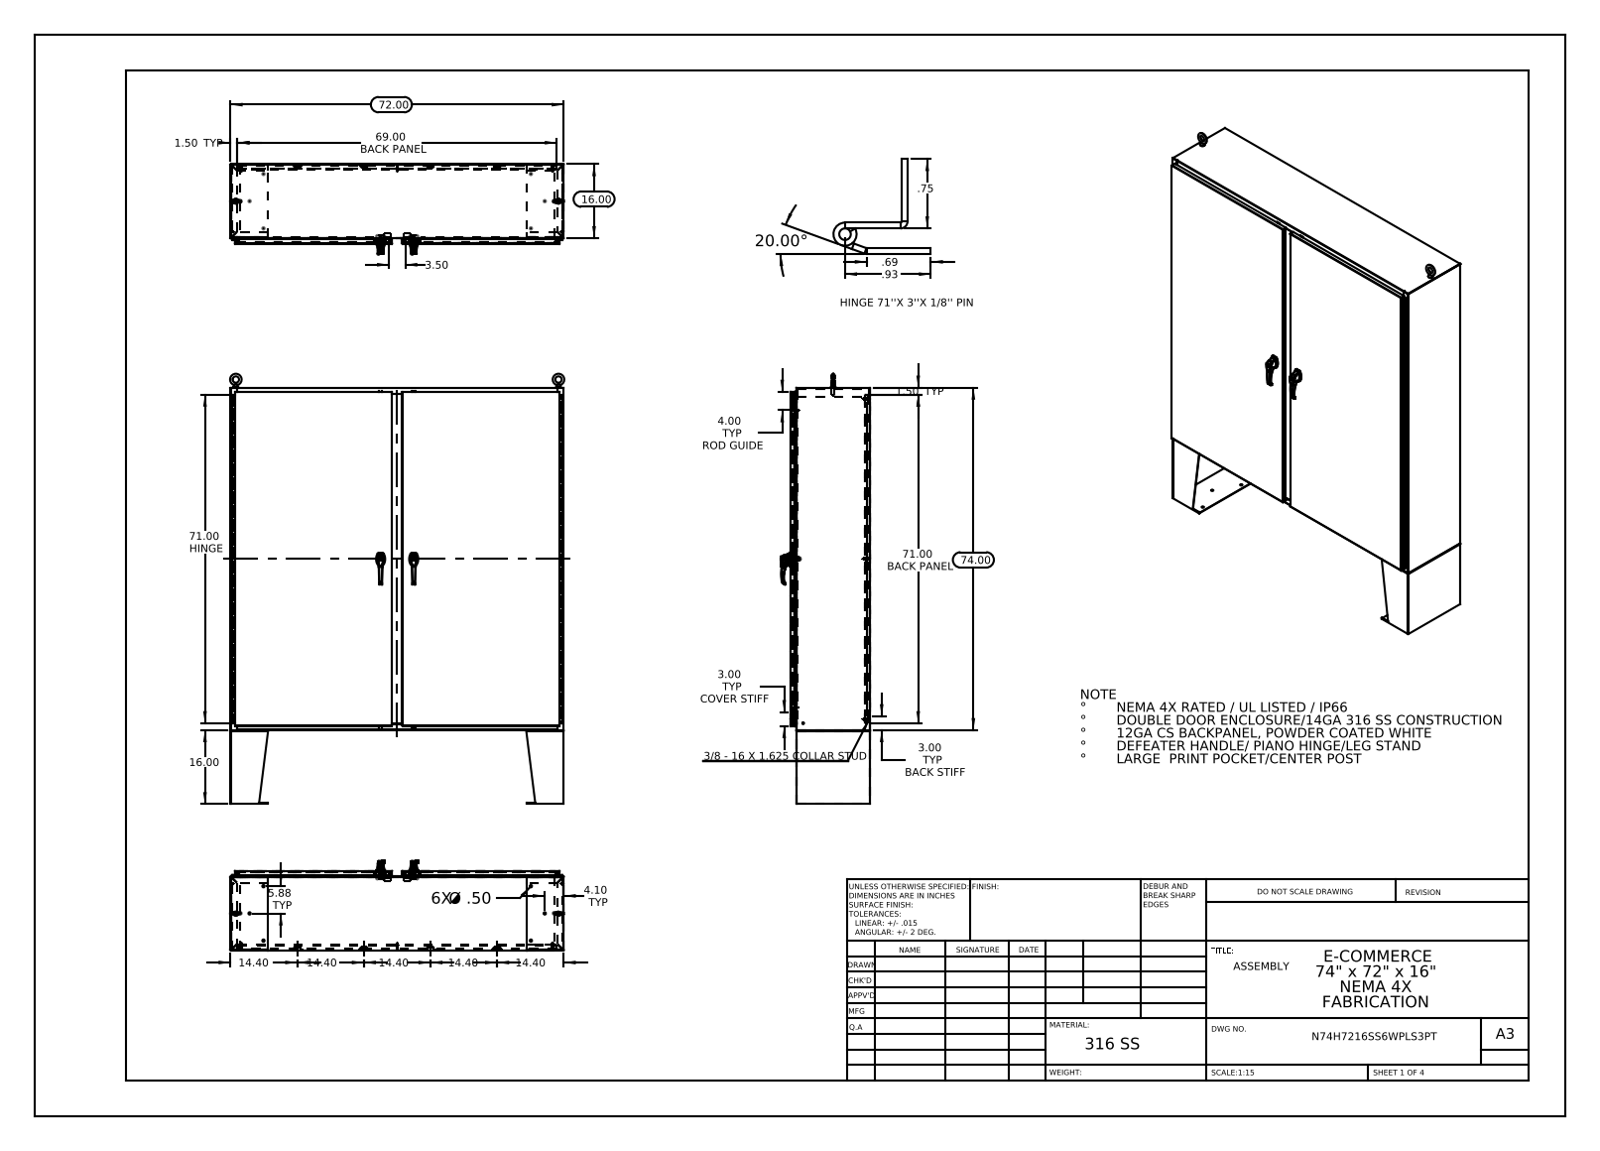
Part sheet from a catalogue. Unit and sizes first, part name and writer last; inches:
Units: inches
Overall size (bounding box): 93 × 72.226 × 19.307
Round holes (diameter × count): ⌀0.25 ×20, ⌀0.5 ×14, ⌀0.138 ×6, ⌀0.161 ×6, ⌀0.079 ×4, ⌀0.313 ×4, ⌀0.437 ×4, ⌀0.75 ×4, ⌀0.125 ×2, ⌀0.125 ×2, ⌀0.197 ×2, ⌀0.203 ×2
Round bosses / shafts (diameter × count): ⌀0.157 ×12, ⌀0.14 ×12, ⌀0.625 ×10, ⌀0.375 ×8, ⌀0.33 ×8, ⌀0.315 ×5, ⌀0.236 ×5, ⌀1.181 ×2
Partial cylindrical surfaces — rounded edges, fillets, slot ends (radius × count): R0.118 ×72, R0.006 ×66, R0.013 ×50, R0.088 ×42, R0.039 ×28, R0.028 ×24, R0.008 ×12, R0.02 ×12
Main face-to-face distances: 0.075, 17.126, 0.104, 17.051, 1.075, 17.201, 1, 16.051, 16.126, 1.179
Hole centre spacings: 7.152, 30.364, 0.295, 0.625, 0.841, 1.313, 1.561, 7.156
Volume: 2 048 in³ · Surface area: 49 772 in²
Bodies: 83 solids, 7630 faces (3104 planar, 3066 cylindrical, 1460 other)
Part name (STEP PRODUCT): 00005090; 00005310_26163101; N74H7216SSWPLS3PT Enclosure Stiffener 14 GA; N74H7216SSWPLS3PT FSD_DD-LSK - Base (+8 more)
STEP written by: SolidWorks 2013 (CONFIG_CONTROL_DESIGN)
